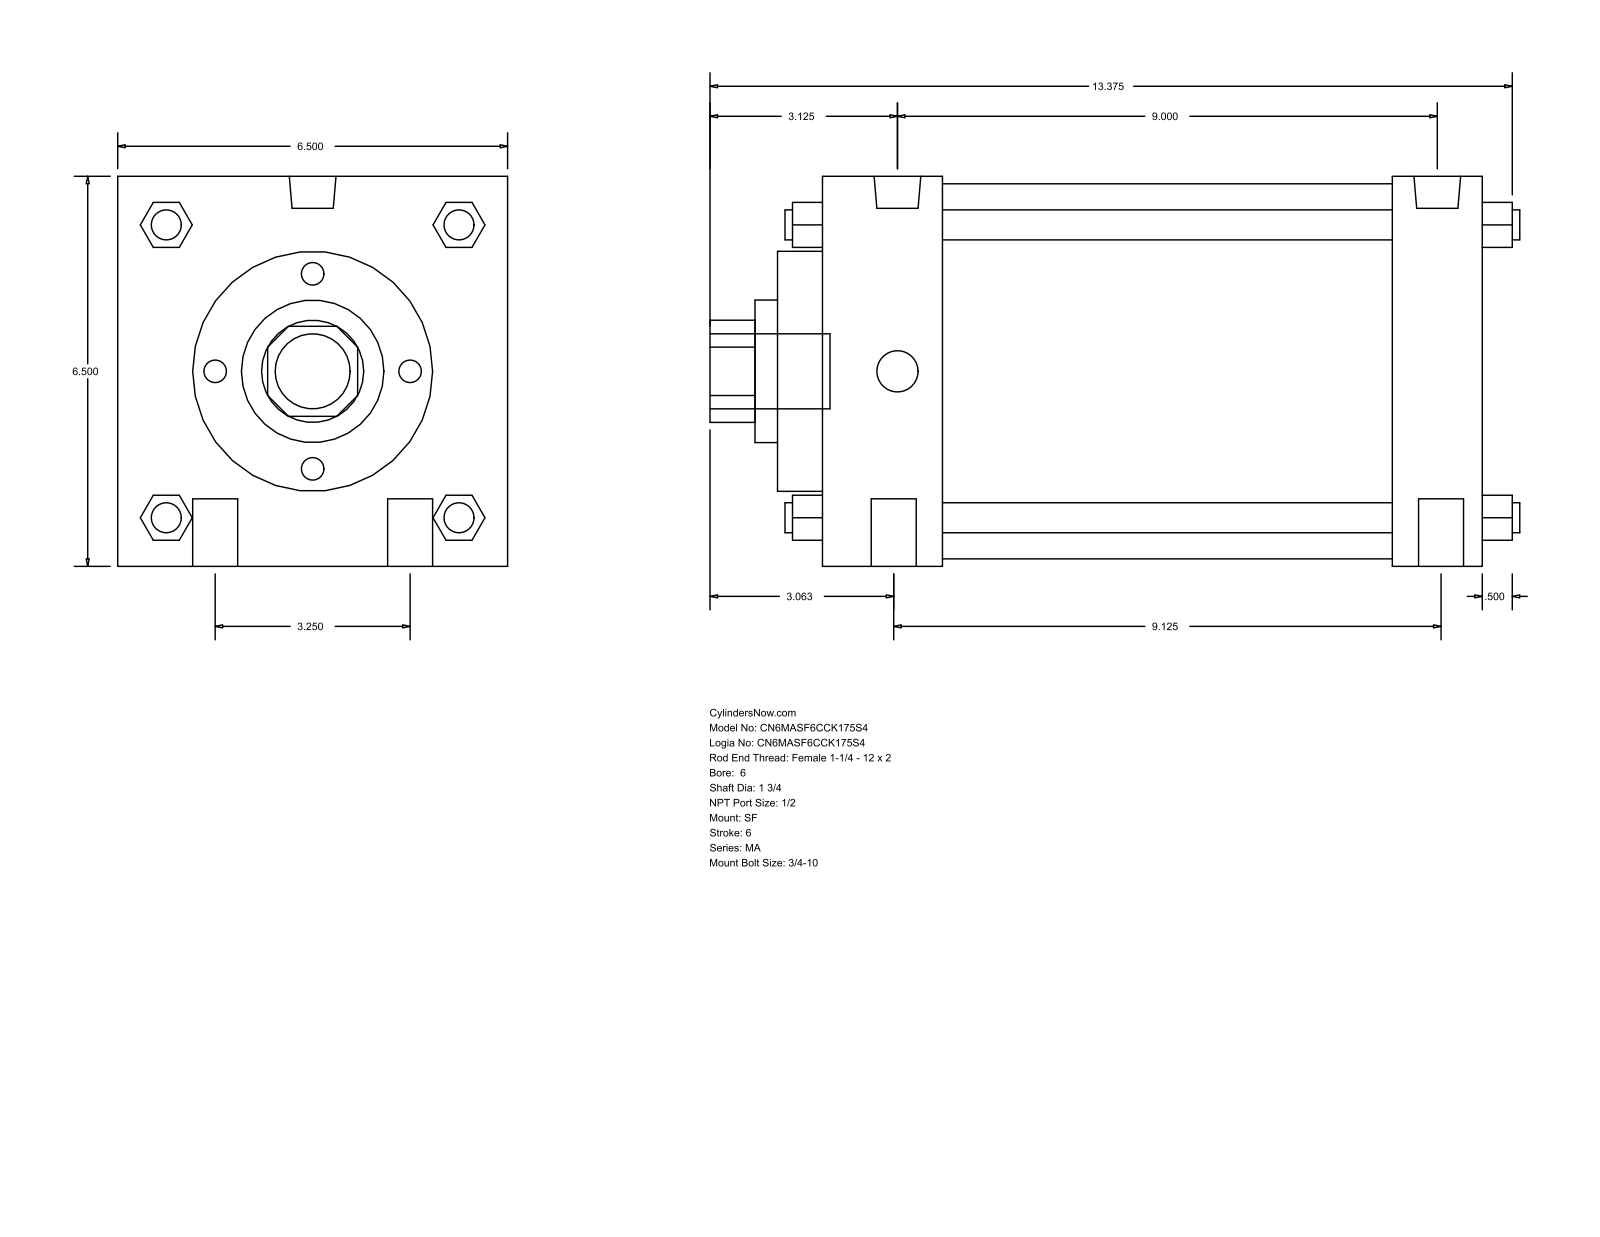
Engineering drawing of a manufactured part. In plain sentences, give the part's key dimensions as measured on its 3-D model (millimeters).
The part is named "MA_SF__0600_1.75". Its 3-D file was written by "GSSL Pune (CONFIG_CONTROL_DESIGN)". It is 0 solids with 126 faces: 95 planar, 31 cylindrical and 0 other. Overall it measures 342.9 by 165.1 by 165.1 millimeters. Round holes: 1 of diameter 44.45, 1 of diameter 60.33, 1 of diameter 101.6, 1 of diameter 158.75. Round bosses or shafts: 4 of diameter 19.05, 4 of diameter 12.7, 2 of diameter 19.77, 2 of diameter 17.46, 1 of diameter 31.75. Partial cylindrical surfaces (rounded edges, fillets, slot ends): 1 of radius 21.63. The main face-to-face distances are 165.1, 279.4, 19.05, 50.8, 241.31, 38.09, 190.51, 228.6, 69.85, 260.36.
